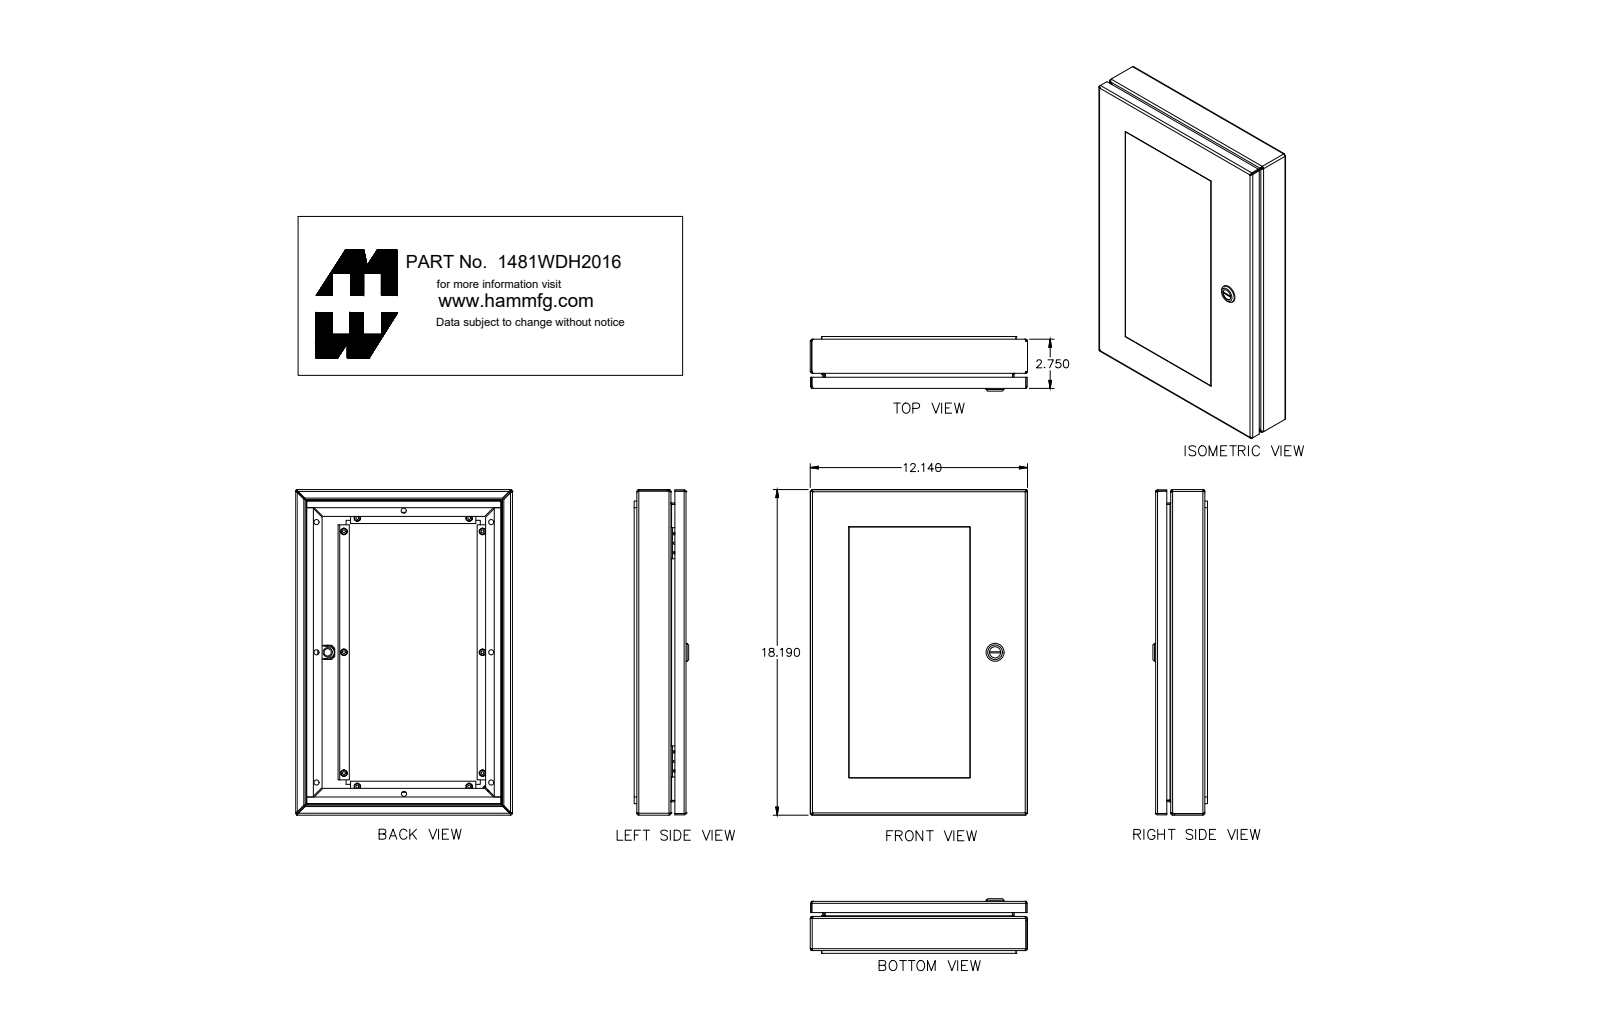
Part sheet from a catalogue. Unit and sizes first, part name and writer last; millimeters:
Units: millimetres
Overall size (bounding box): 462 × 308.4 × 73.9
Round holes (diameter × count): ⌀3.3 ×10, ⌀7.1 ×8, ⌀3.5 ×2, ⌀5.9 ×1, ⌀6.1 ×1, ⌀6.1 ×1, ⌀15.9 ×1, ⌀19.9 ×1
Round bosses / shafts (diameter × count): ⌀9.3 ×10, ⌀5.7 ×10, ⌀4.2 ×10, ⌀27.9 ×1, ⌀13.3 ×1, ⌀11.6 ×1, ⌀10.1 ×1, ⌀9 ×1
Partial cylindrical surfaces — rounded edges, fillets, slot ends (radius × count): R0.9 ×28, R2.7 ×28, R2.6 ×20, R0.4 ×4, R2.2 ×4, R3.2 ×2, R0.5 ×1, R0.7 ×1
Main face-to-face distances: 1.8, 6.4, 4.5, 65.5, 21.4, 44.1, 59.1, 306.5, 15, 67.3
Hole centre spacings: 125, 171.5, 178.8, 261.1, 405, 196.9, 248, 26.9
Volume: 975 800 mm³ · Surface area: 778 700 mm²
Bodies: 41 solids, 984 faces (531 planar, 275 cylindrical, 178 other)
Part name (STEP PRODUCT): 1481WDH2016_Default
STEP written by: SolidWorks 2019 (CONFIG_CONTROL_DESIGN)
